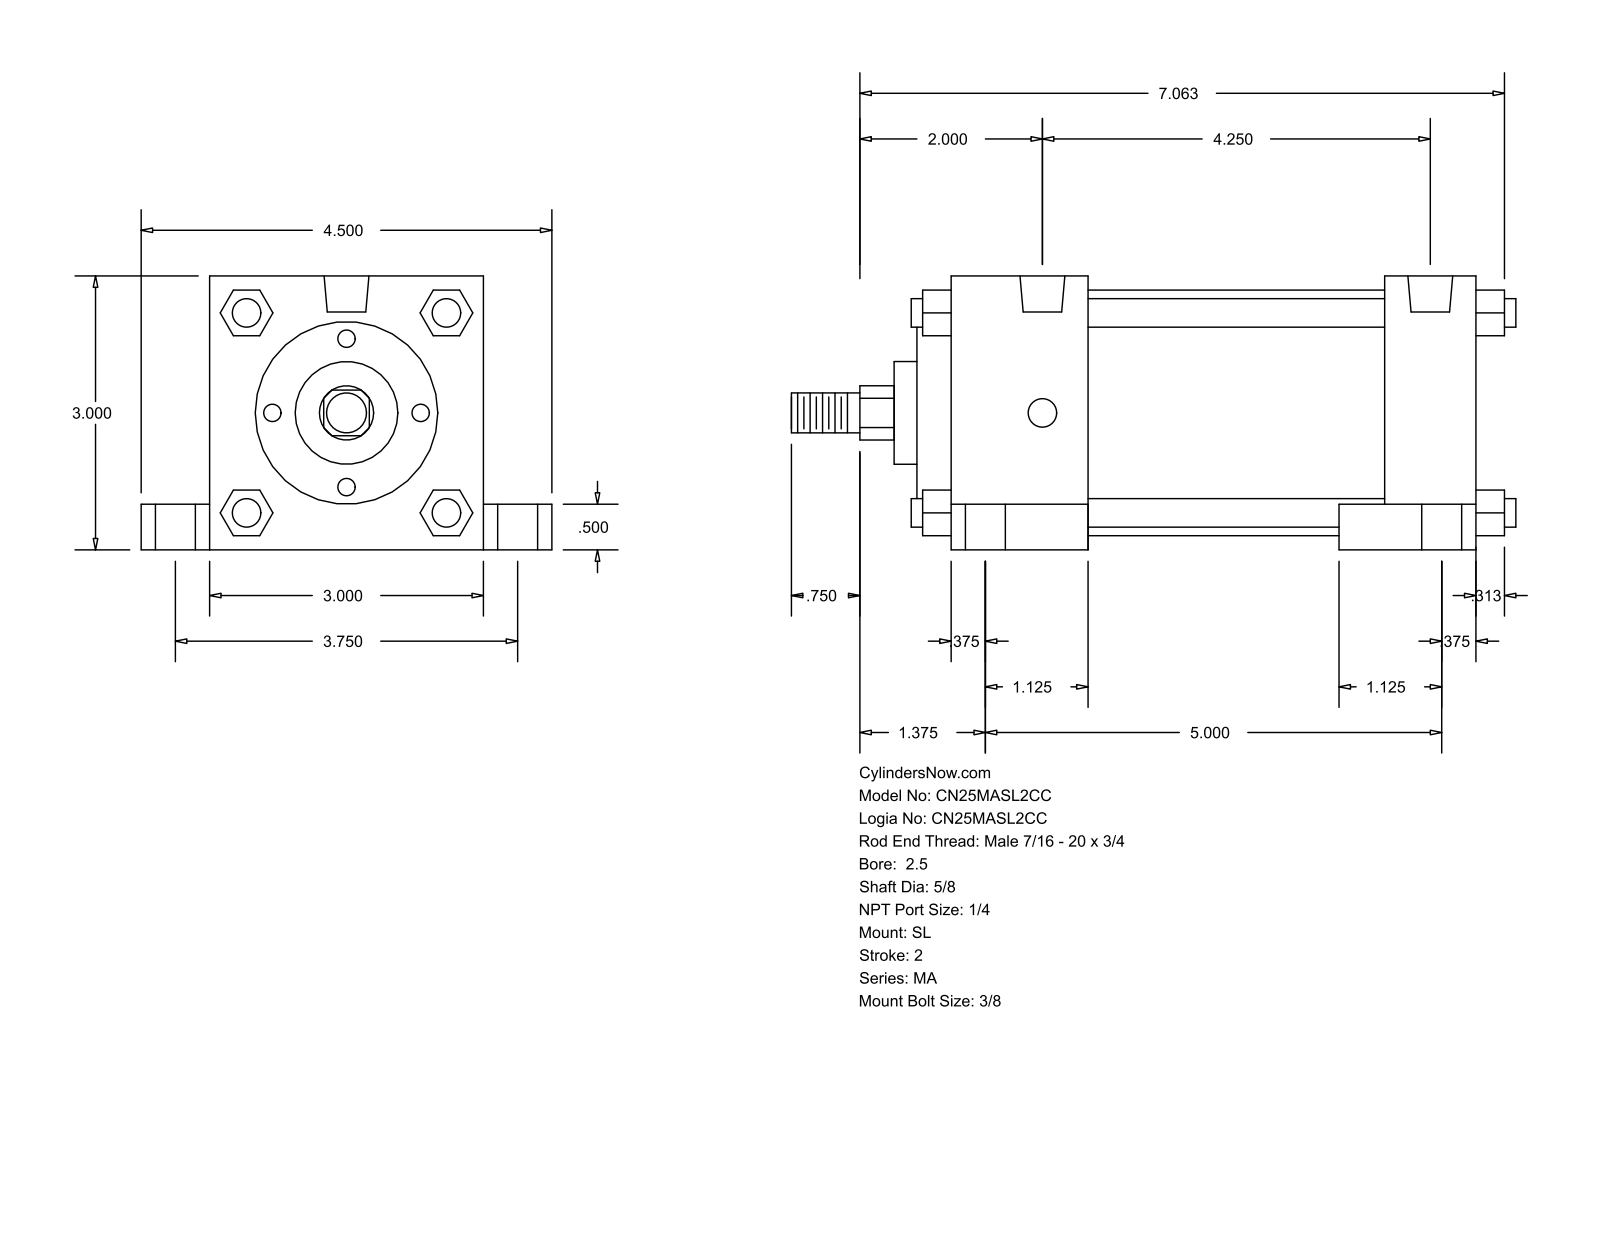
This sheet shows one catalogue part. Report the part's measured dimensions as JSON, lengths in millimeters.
{"part_name": "MA_SL__0250_0.625", "step_written_by": "GSSL Pune (CONFIG_CONTROL_DESIGN)", "units": "millimeters", "bodies": {"solids": 0, "faces": 150, "planar": 113, "cylindrical": 37, "other": 0}, "overall_size": [201.61, 114.3, 76.2], "round_holes": [[7.94, 4], [11.11, 4], [17.46, 4], [12.49, 2]], "round_bosses_or_shafts": [[7.94, 4], [68.33, 1], [50.8, 1], [28.57, 1], [15.88, 1], [11.11, 1]], "partial_cylinders_radius": [[7.54, 1]], "face_to_face_distances": [76.2, 146.05, 12.7, 82.55, 25.4, 38.1, 107.95, 120.65, 19.05, 63.5], "hole_center_spacings": [47.73, 50.2, 95.24, 107.95, 120.9, 127.01, 132.67, 158.75]}
